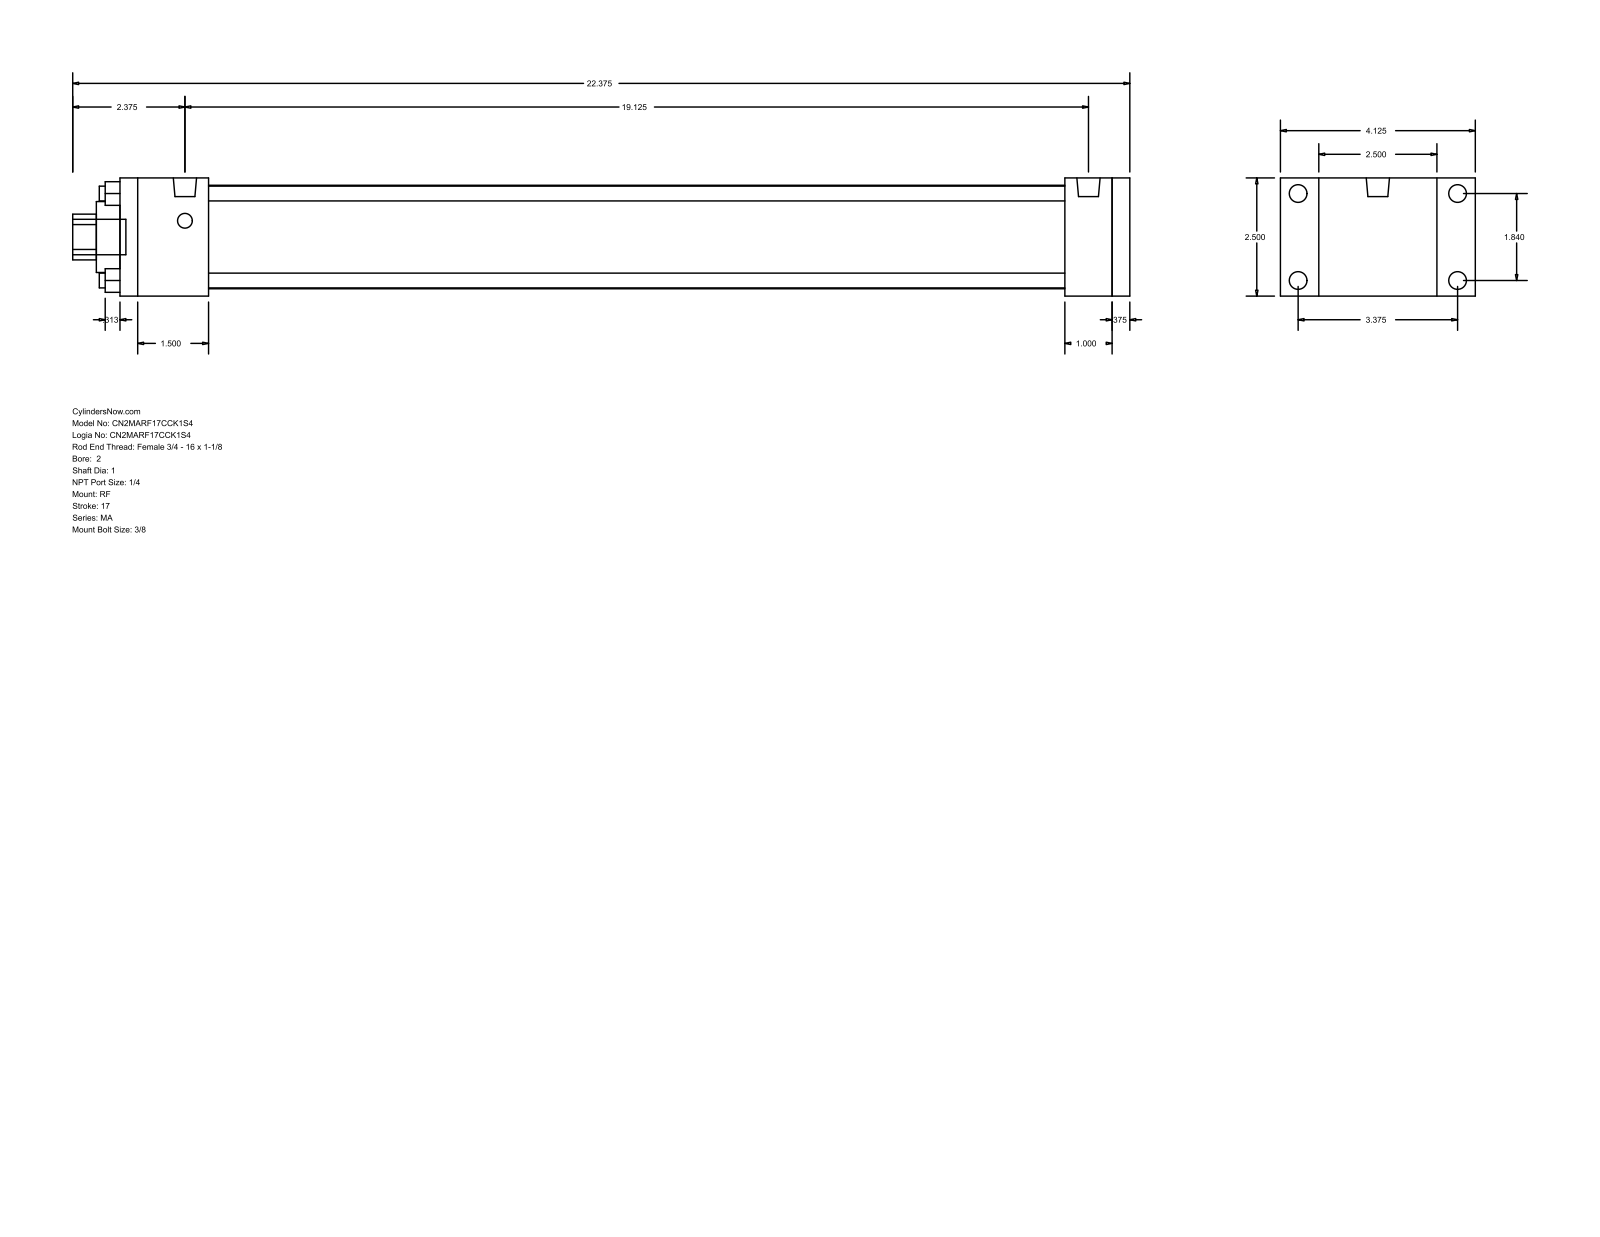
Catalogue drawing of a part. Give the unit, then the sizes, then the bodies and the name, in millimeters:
Units: millimetres
Overall size (bounding box): 568.33 × 104.78 × 63.5
Round holes (diameter × count): ⌀7.94 ×4, ⌀25.4 ×1, ⌀38.1 ×1, ⌀55.63 ×1
Round bosses / shafts (diameter × count): ⌀9.53 ×4, ⌀7.94 ×4, ⌀12.49 ×2, ⌀19.05 ×1
Partial cylindrical surfaces — rounded edges, fillets, slot ends (radius × count): R12.29 ×1
Main face-to-face distances: 63.5, 533.4, 9.53, 542.93, 25.4, 20.64, 12.7, 47.63, 485.77, 495.3
Hole centre spacings: 33.05, 46.74, 66.1
Bodies: 0 solids, 92 faces (64 planar, 28 cylindrical, 0 other)
Part name (STEP PRODUCT): MA_RF__0200_1
STEP written by: GSSL Pune (CONFIG_CONTROL_DESIGN)
